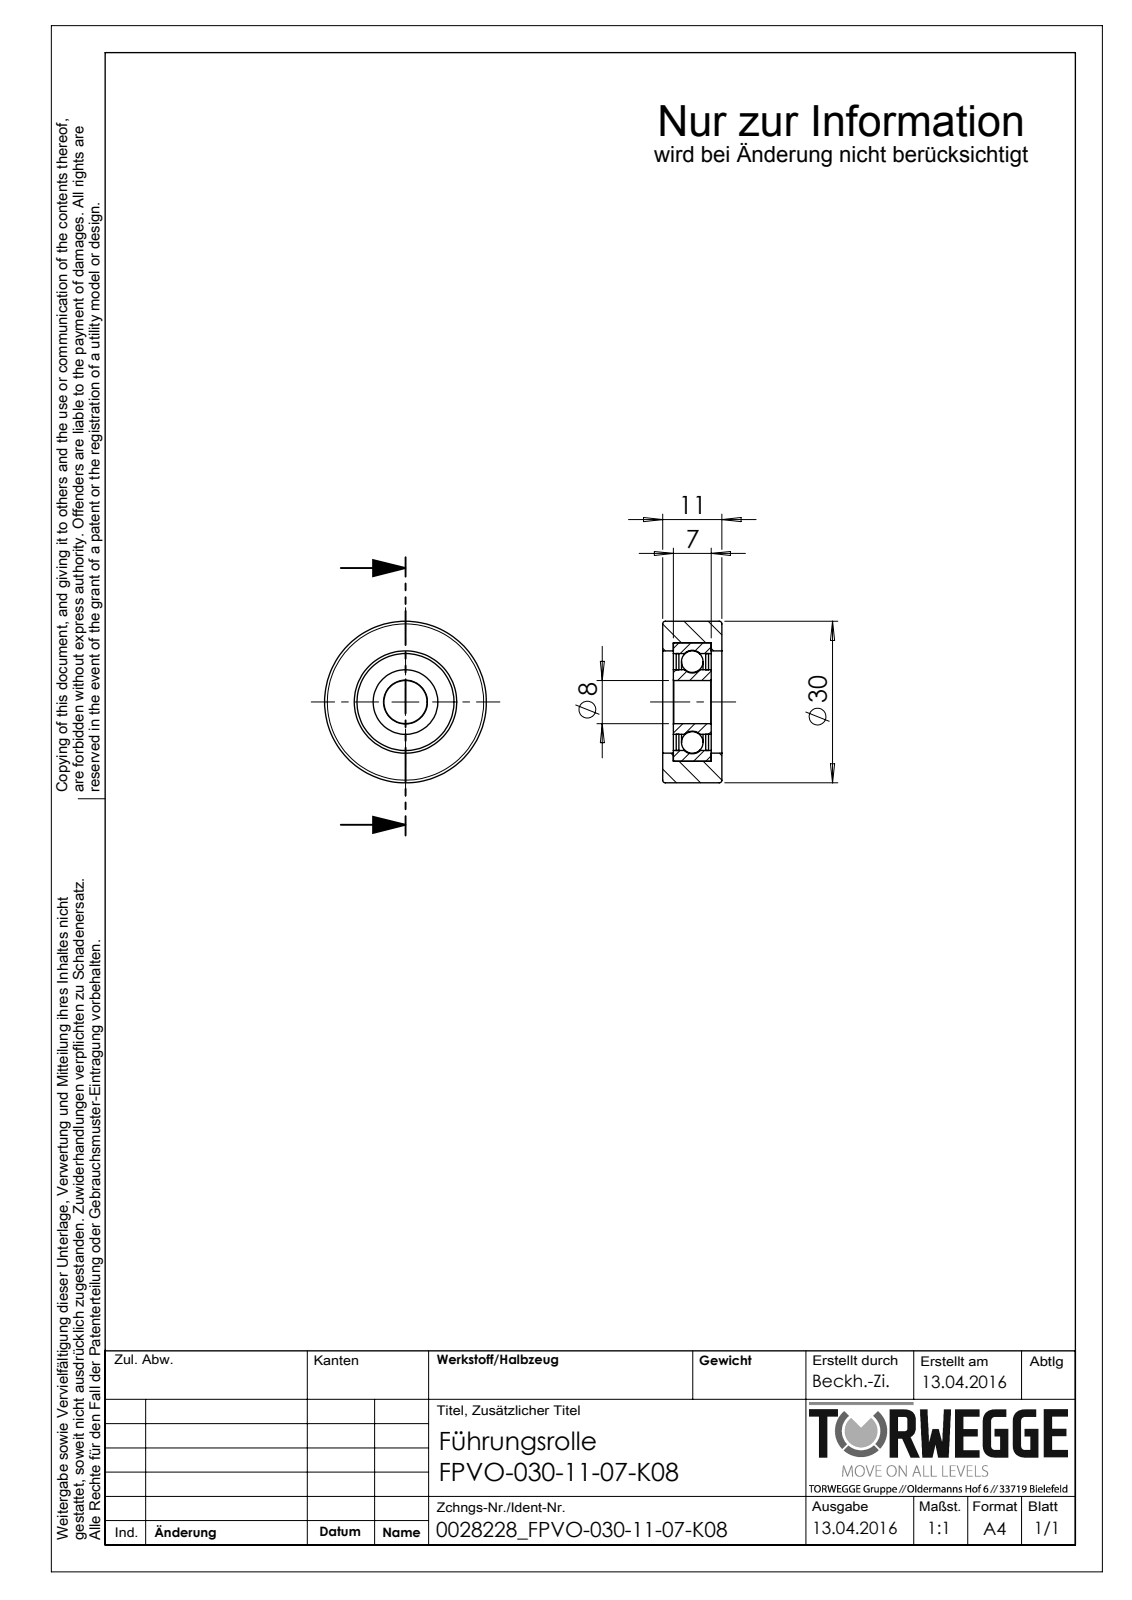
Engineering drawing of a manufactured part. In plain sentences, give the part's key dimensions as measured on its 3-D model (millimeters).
The part is named "0028228_FPVO-030-11-07-K08". Its 3-D file was written by "SolidWorks 2016 (AUTOMOTIVE_DESIGN)". It is 6 solids with 62 faces: 12 planar, 28 cylindrical and 22 other. Overall it measures 30 by 30 by 11 millimeters. Its volume is 5 909 cubic millimeters and its surface area 5 729 square millimeters. Round holes: 1 of diameter 8, 1 of diameter 12, 1 of diameter 18, 1 of diameter 19, 1 of diameter 22. Round bosses or shafts: 1 of diameter 30. The main face-to-face distances are 0.5, 2, 9, 6, 11, 2.5, 3, 8, 8.5, 1.
